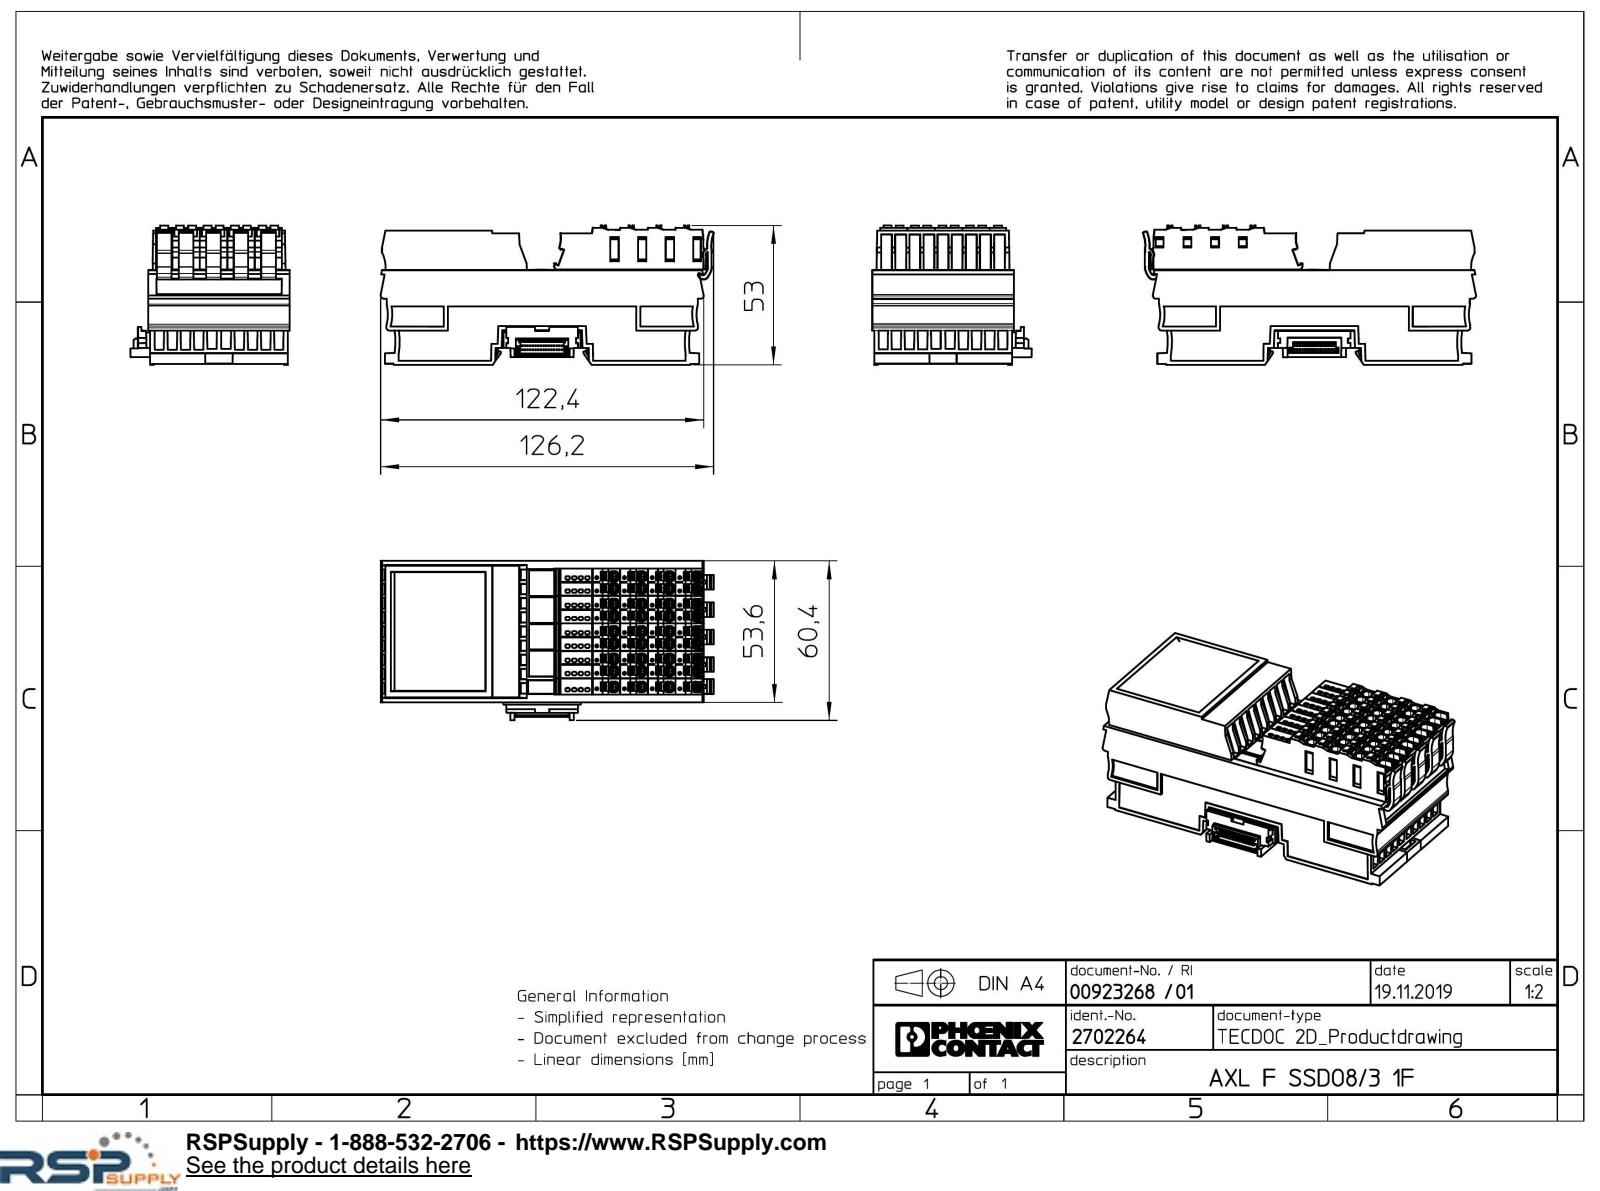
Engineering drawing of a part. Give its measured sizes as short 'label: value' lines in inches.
name: FIBO-P-SP-TWIN-...-YE.04; FIBO_COLOR_CODE_RD3000-select; FIBO-P-SP1.5-SINGLE-PWR; FIBO_F_YE1018-select (+7 more)
written by: Creo Elements/Direct Modeling 20.1A 29-Sep-2018 (C) Parametric Technology GmbH (AUTOMOTIVE_DESIGN)
unit: in
bodies: 13 solids, 5109 faces (4231 planar, 656 cylindrical, 222 other)
size: 4.967 × 2.378 × 2.078
volume: 16.69 in³; area: 132.8 in²
holes: 36× ⌀0.047
rounds: 147× R0.02, 130× R0.059, 36× R0.049, 8× R0.039, 6× R0.496, 5× R0.012, 5× R0.118, 2× R0.007
face distances: 0.409, 0.819, 0.413, 2.075, 0.035, 1.228, 0.406, 1.396, 0.815, 0.522
hole spacings: 0.582, 0.413, 0.409, 0.458, 0.922, 0.917, 0.465, 0.734
